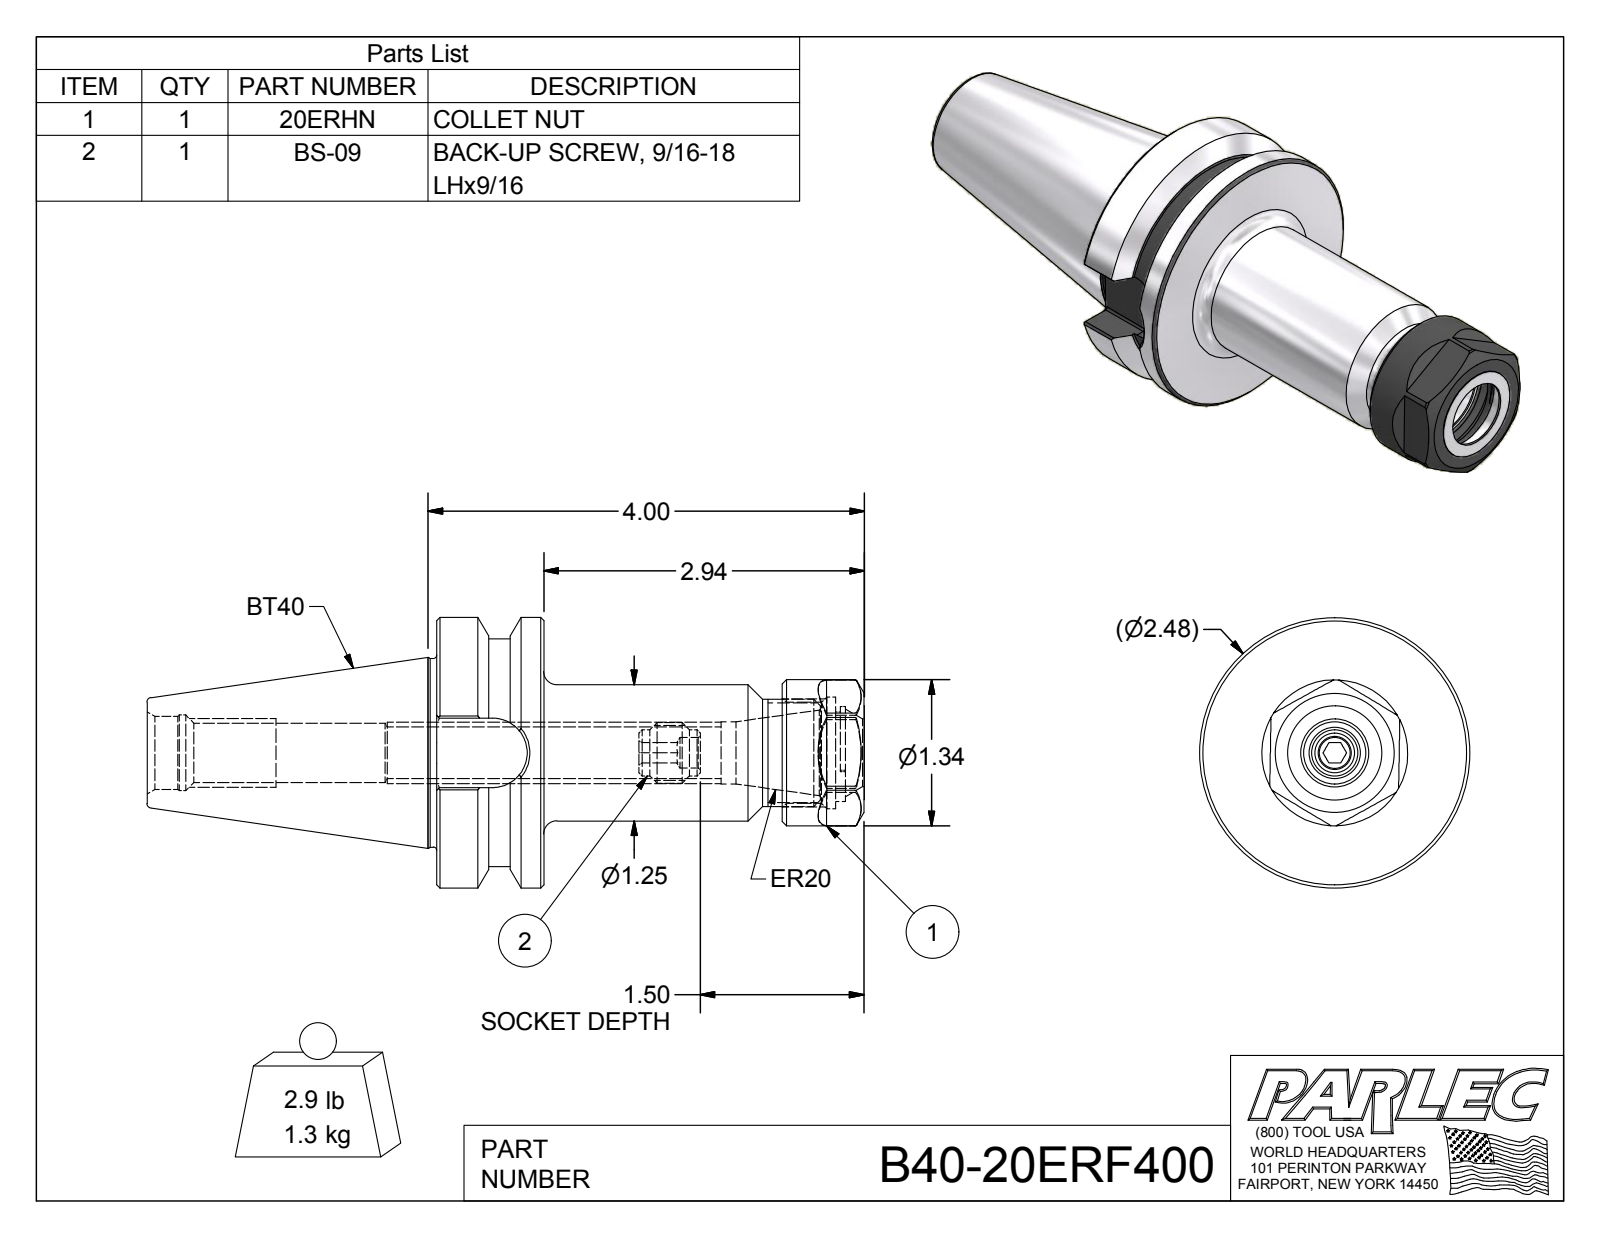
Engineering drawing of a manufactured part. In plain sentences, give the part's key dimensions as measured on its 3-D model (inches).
The part is named "B40-20ER4-1; 20ERHN; BS-09; B40-20ERF400". Its 3-D file was written by "Autodesk Inventor 2016 (AUTOMOTIVE_DESIGN)". It is 3 solids with 130 faces: 55 planar, 34 cylindrical and 41 other. Overall it measures 6.575 by 2.48 by 2.48 inches. Its volume is 10.12 cubic inches and its surface area 55.59 square inches. Round holes: 1 of diameter 0.281, 1 of diameter 0.472, 1 of diameter 0.545, 1 of diameter 0.57, 1 of diameter 0.61, 1 of diameter 0.67, 1 of diameter 0.694, 1 of diameter 0.925, 1 of diameter 1.024. Round bosses or shafts: 1 of diameter 2.48, 1 of diameter 2.087, 1 of diameter 1.73, 1 of diameter 1.339, 1 of diameter 1.25, 1 of diameter 0.984, 1 of diameter 0.555, 1 of diameter 0.422. Partial cylindrical surfaces (rounded edges, fillets, slot ends): 8 of radius 0.02, 1 of radius 0.319, 1 of radius 0.373, 1 of radius 0.415, 1 of radius 0.423. The main face-to-face distances are 0.984, 3.922, 2.938, 3.171, 2.187, 0.751, 1.78, 1.181, 3.658, 2.674.
